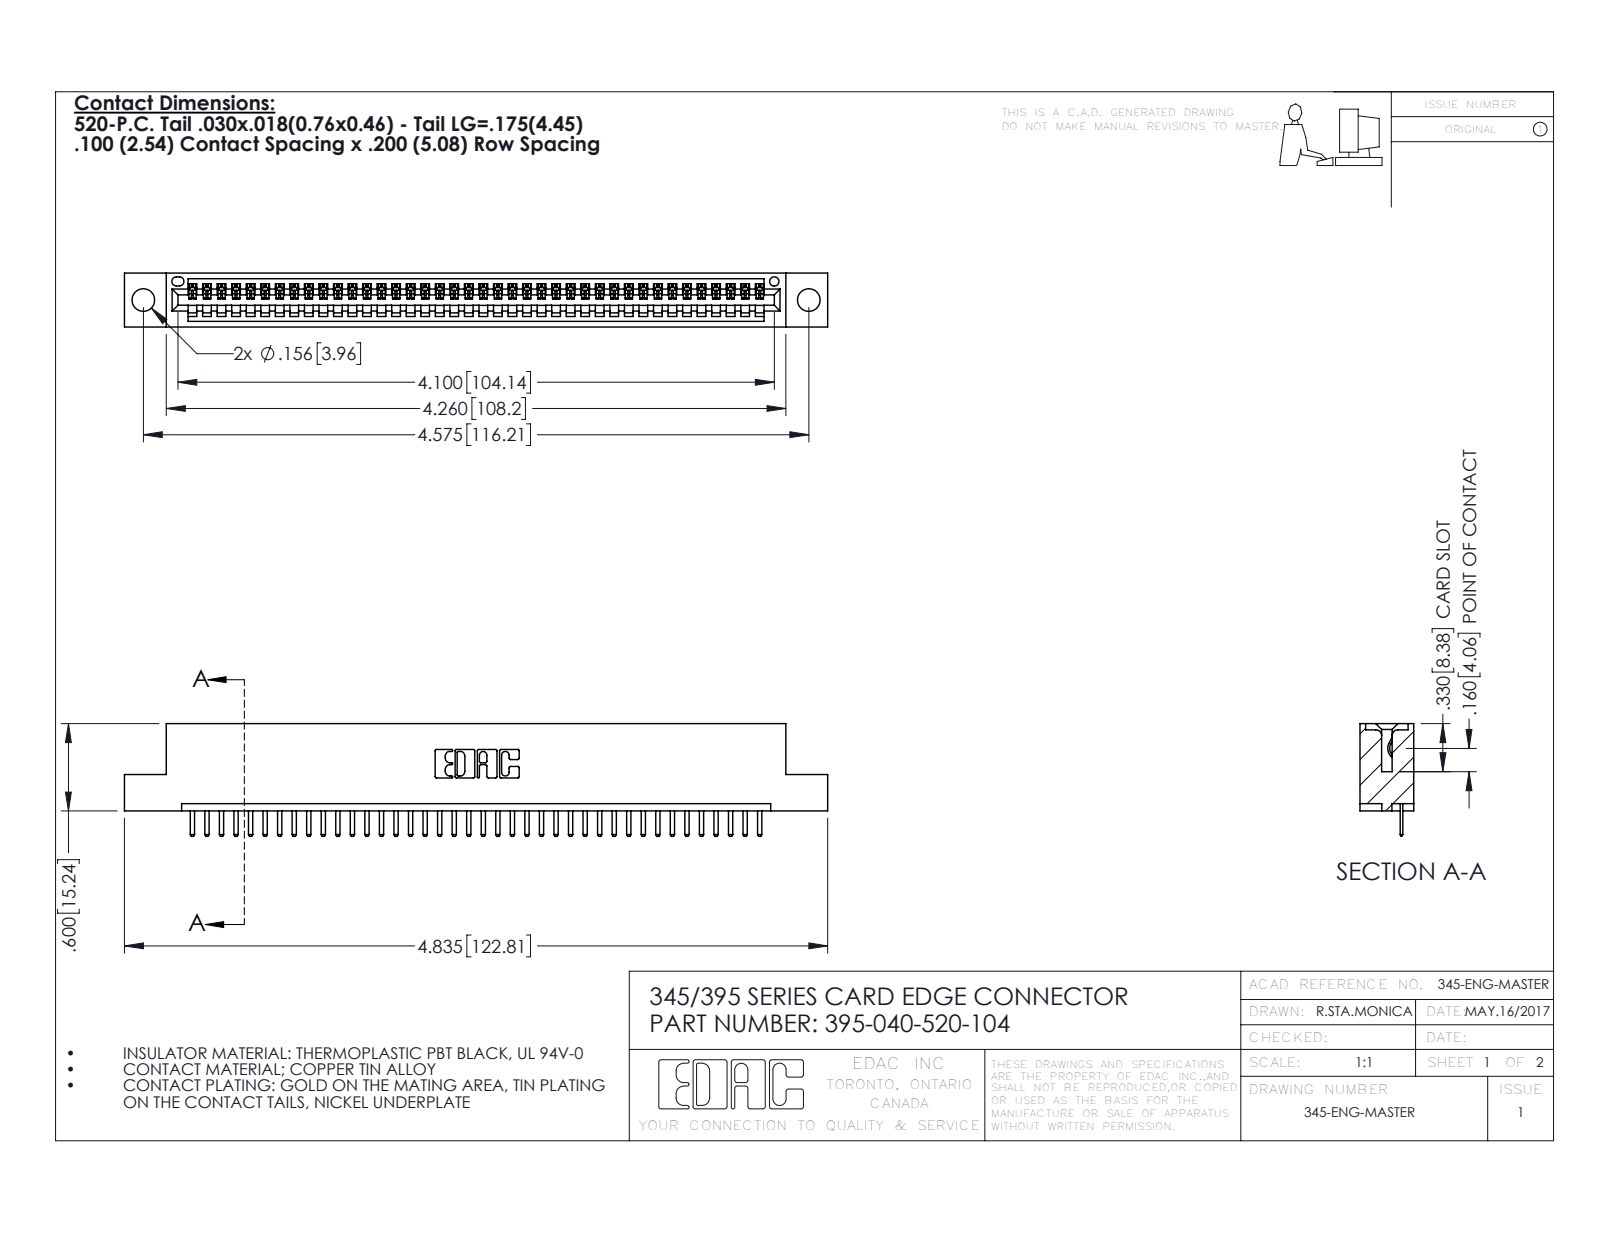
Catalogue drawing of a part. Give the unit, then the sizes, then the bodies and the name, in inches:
Units: inches
Overall size (bounding box): 4.835 × 0.775 × 0.37
Round holes (diameter × count): ⌀0.156 ×2, ⌀0.064 ×1
Partial cylindrical surfaces — rounded edges, fillets, slot ends (radius × count): R0.01 ×82, R0.006 ×80, R0.01 ×22, R0.007 ×6, R0.031 ×6, R0.026 ×3, R0.031 ×2, R0.04 ×2
Main face-to-face distances: 0.298, 0.072, 0.37, 0.2, 0.098, 0.272, 0.025, 0.225, 0.072, 0.149
Hole centre spacings: 0.27, 4.339, 4.575
Volume: 0.698 in³ · Surface area: 22.65 in²
Bodies: 41 solids, 2606 faces (1760 planar, 846 cylindrical, 0 other)
Part name (STEP PRODUCT): 395-040-520-104; 345-292-001_345-293-120; 345 Part_Flush Mounting Lugs - 0.156 Dia-TH
STEP written by: SolidWorks 2016 (CONFIG_CONTROL_DESIGN)
